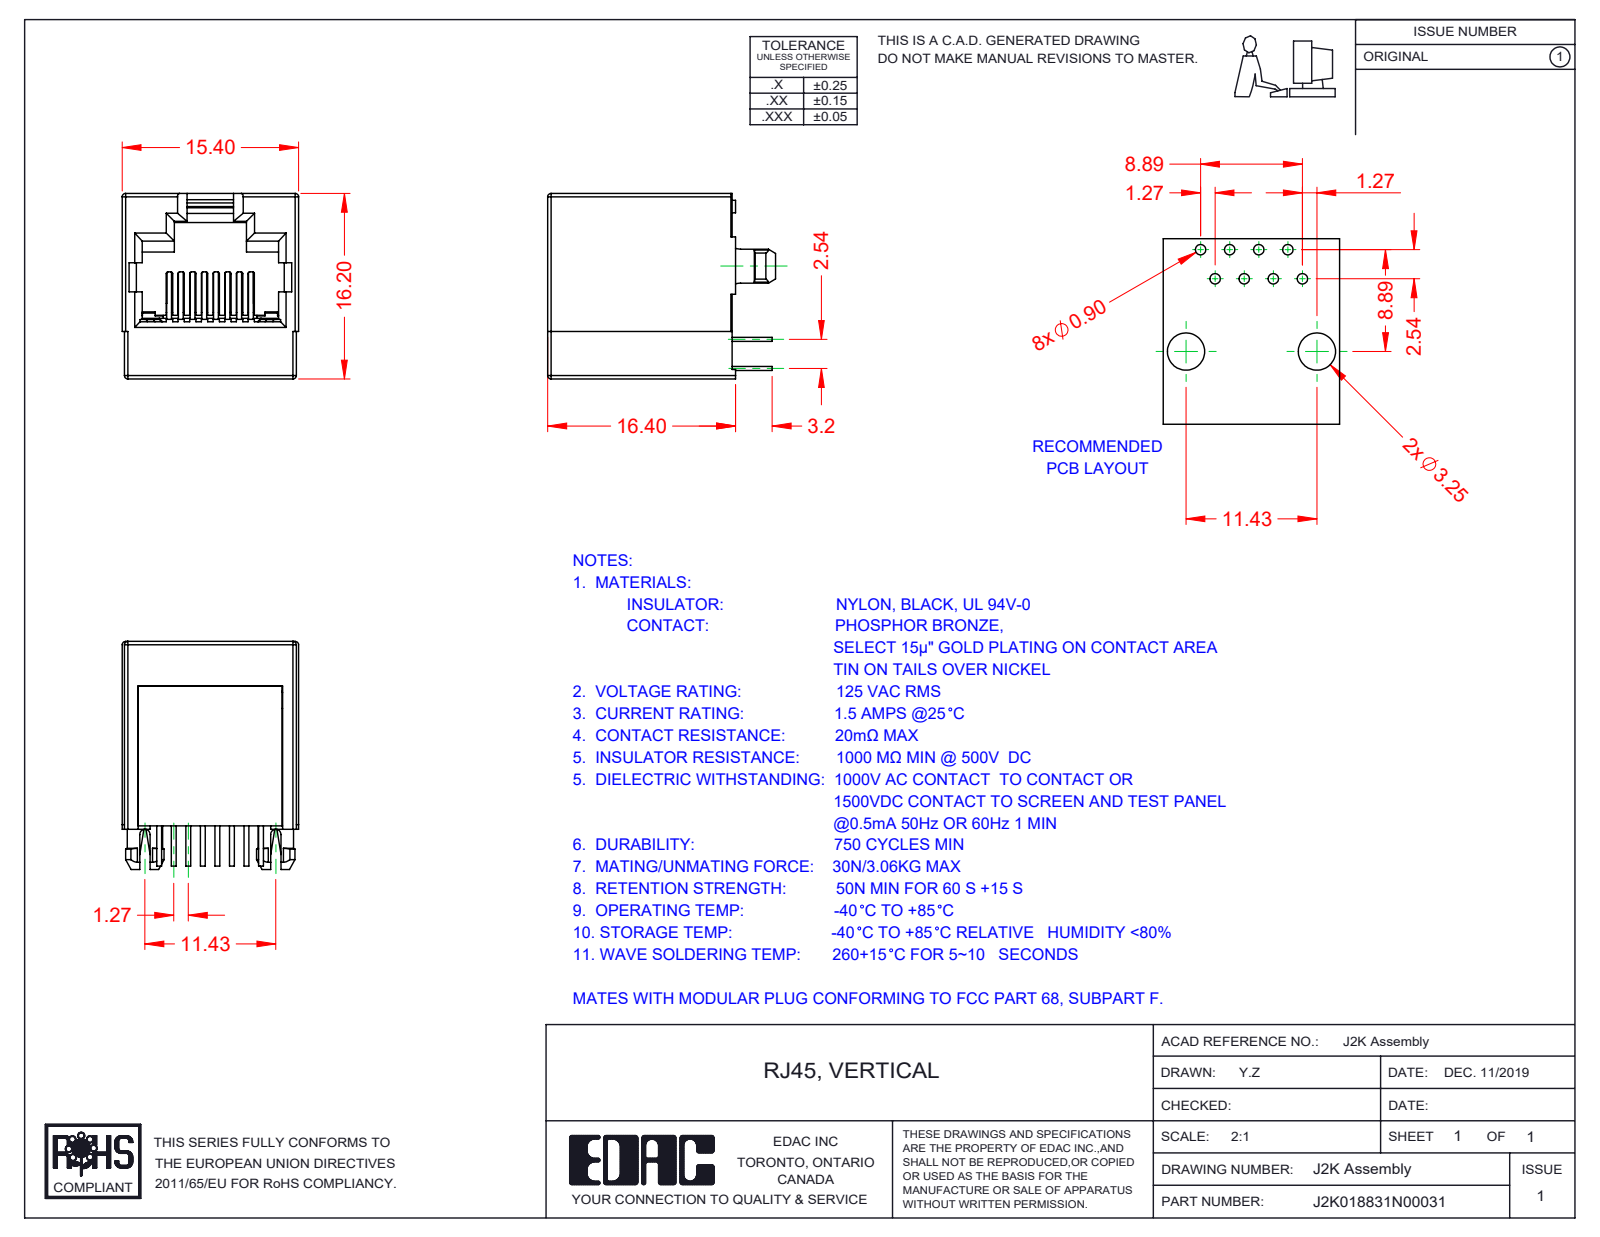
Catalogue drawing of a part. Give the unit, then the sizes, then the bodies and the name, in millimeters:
Units: millimetres
Overall size (bounding box): 19.9 × 16.2 × 15.4
Round bosses / shafts (diameter × count): ⌀3.1 ×2, ⌀1.1 ×2
Partial cylindrical surfaces — rounded edges, fillets, slot ends (radius × count): R0.15 ×16, R0.3 ×10, R0.5 ×3, R0.1 ×2, R0.2 ×2, R0.45 ×2, R0.6 ×2, R0.95 ×2
Main face-to-face distances: 16.2, 15.4, 1.4, 14, 1.2, 13.8, 15.2, 0.35, 0.5, 15
Volume: 2 473 mm³ · Surface area: 3 962 mm²
Bodies: 10 solids, 723 faces (586 planar, 113 cylindrical, 24 other)
Part name (STEP PRODUCT): 2K Insulator; RJ2K018831N00031; 2K Contacts; 2K Contact Lock
STEP written by: SolidWorks 2016 (CONFIG_CONTROL_DESIGN)
